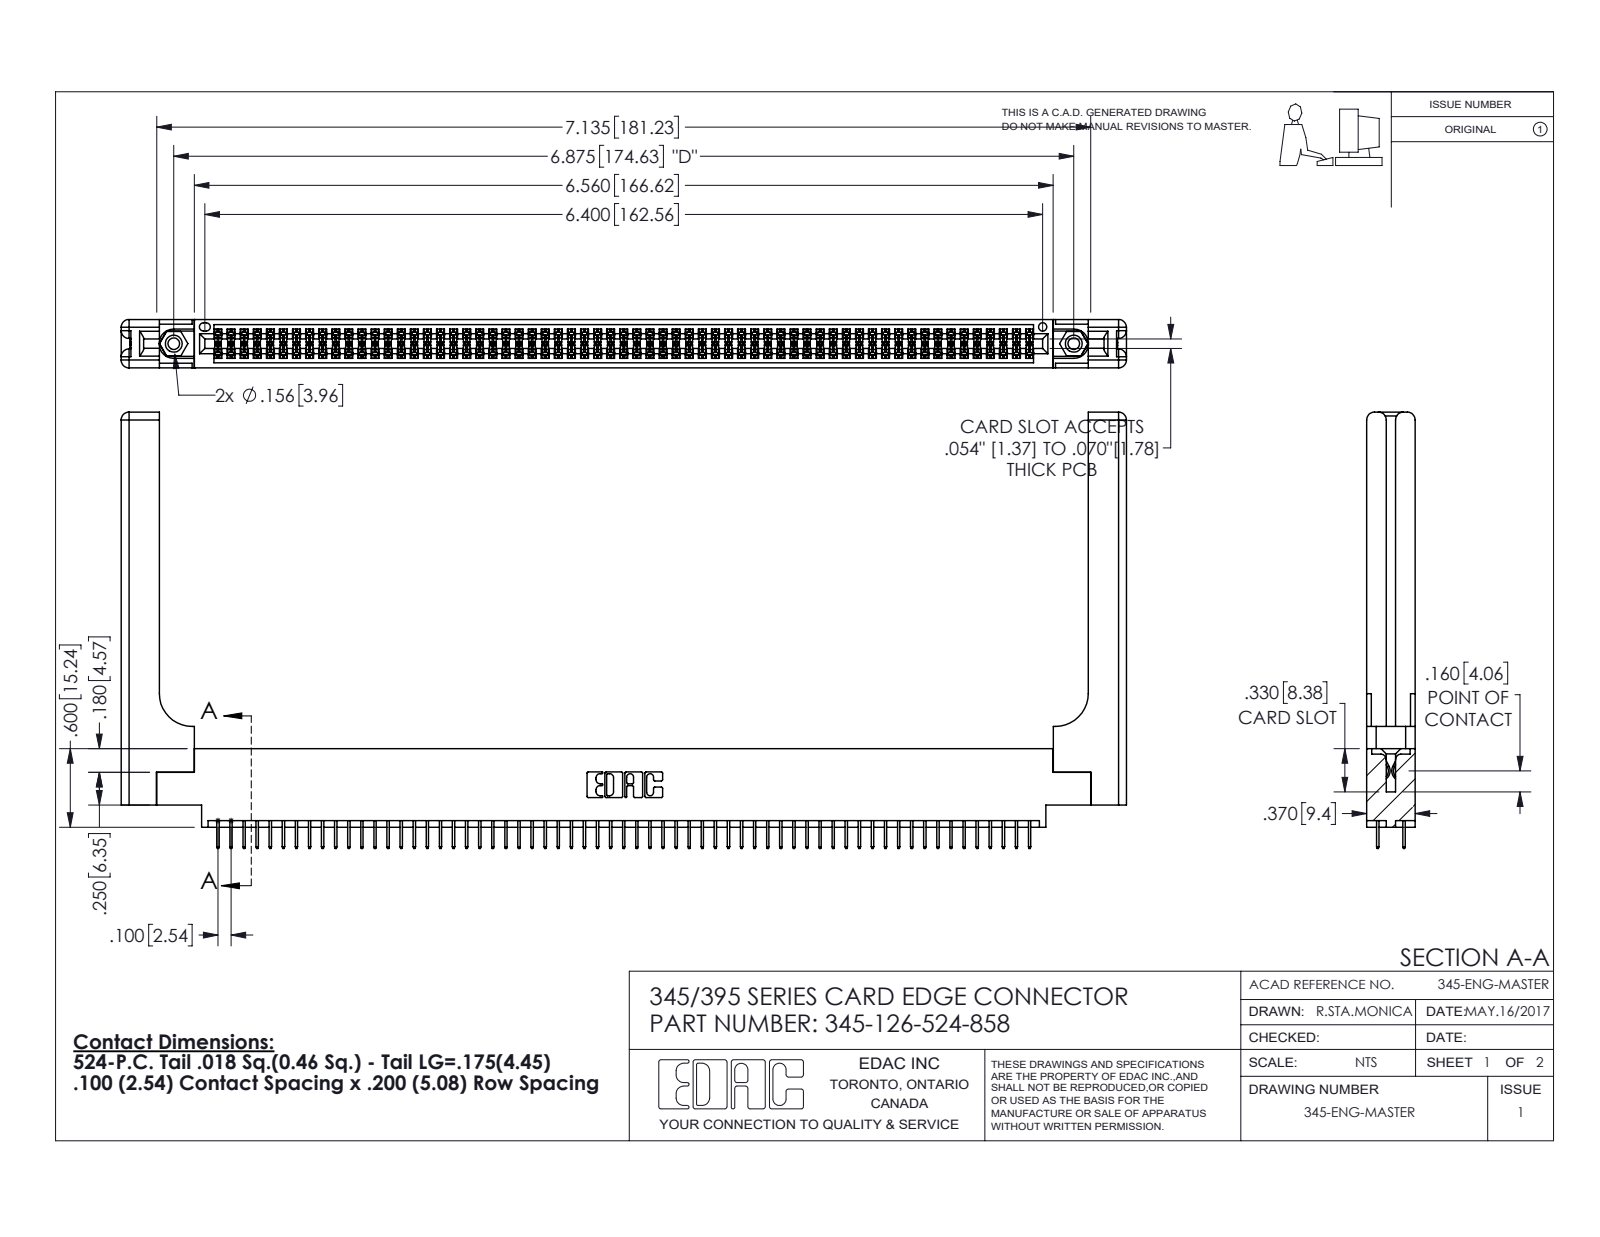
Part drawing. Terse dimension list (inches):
name: 345-250-001_345-250-001-102; 345-220-058_345-220-058; 345 Part_0.170 Offset - 0.156 Dia-TH; 345-292-001_345-293-124 (+1 more)
written by: SolidWorks 2016 (CONFIG_CONTROL_DESIGN)
unit: in
bodies: 131 solids, 7190 faces (5146 planar, 1984 cylindrical, 60 other)
size: 7.679 × 3.332 × 0.37
volume: 1.667 in³; area: 51.07 in²
holes: 2× ⌀0.089, 2× ⌀0.125, 2× ⌀0.156, 1× ⌀0.064
bosses: 2× ⌀0.155
rounds: 189× R0.006, 22× R0.01, 16× R0.06, 6× R0.007, 6× R0.031, 3× R0.026, 2× R0.014, 2× R0.019
face distances: 0.072, 0.37, 0.298, 0.2, 0.098, 0.272, 0.025, 0.225, 0.175, 0.072
hole spacings: 0.27, 6.639, 6.875
